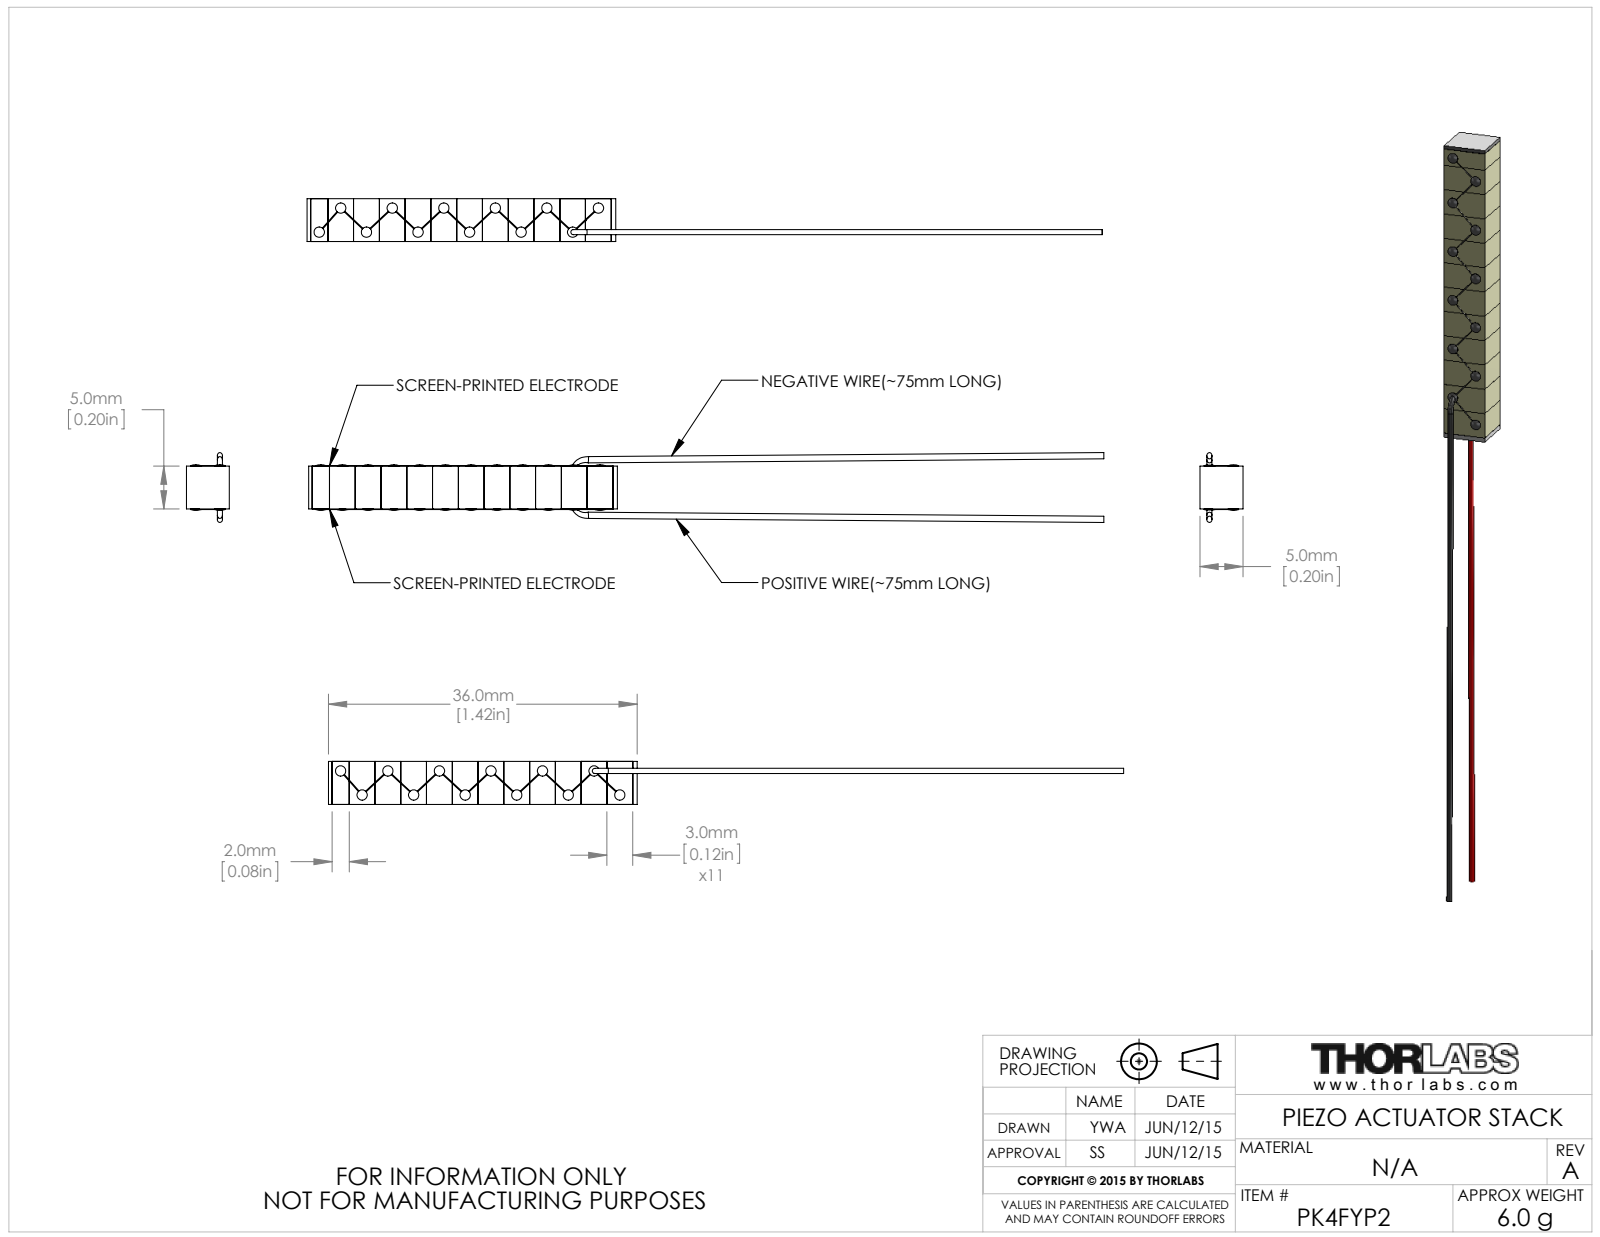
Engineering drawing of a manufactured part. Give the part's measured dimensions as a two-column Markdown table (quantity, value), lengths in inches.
| quantity | value |
| --- | --- |
| part name | CTN002969 |
| STEP written by | SolidWorks 2014 (AUTOMOTIVE_DESIGN) |
| units | inches |
| bodies | 33 solids, 284 faces (136 planar, 92 cylindrical, 56 other) |
| overall size | 3.644 × 0.32 × 0.197 |
| volume | 0.07 in³ |
| surface area | 3.204 in² |
| round bosses / shafts (diameter × count) | 0.047 × 12 |
| main face-to-face distances | 0.118, 0.197, 0.236, 0.354, 0.472, 0.591, 0.709, 0.827, 0.945, 1.063 |
